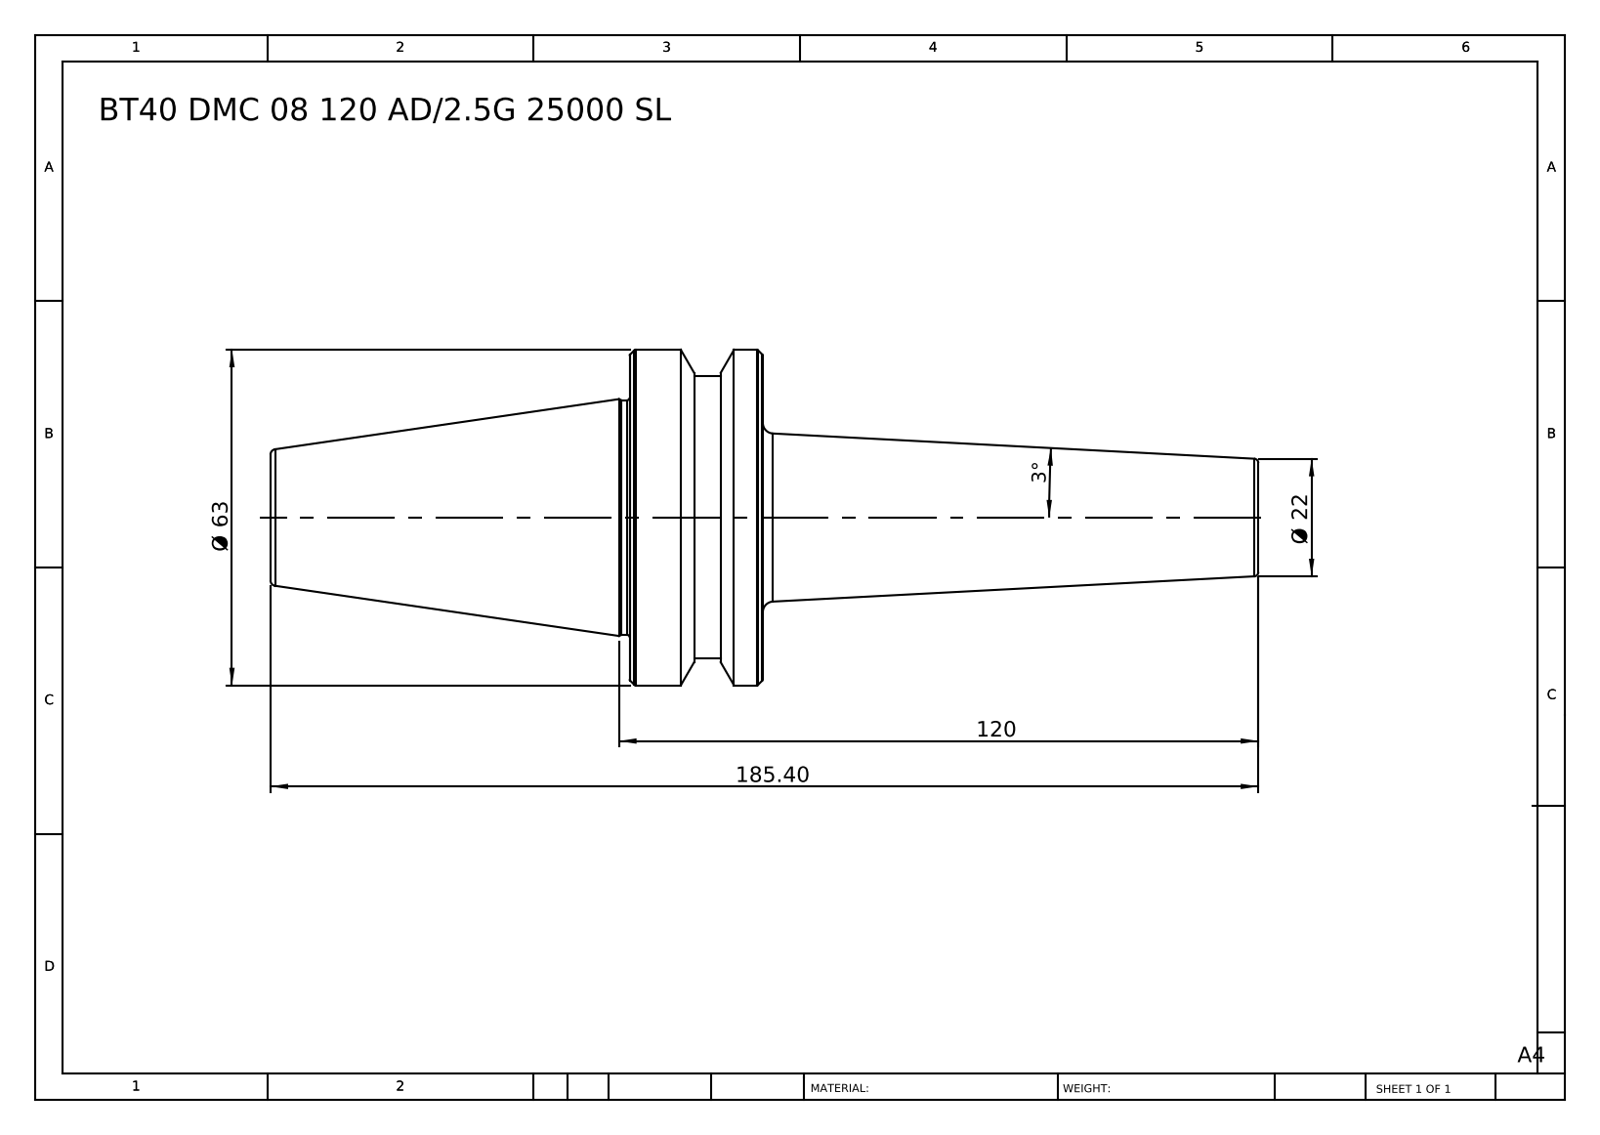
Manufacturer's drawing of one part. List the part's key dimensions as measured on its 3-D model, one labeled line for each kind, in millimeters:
Part name (STEP PRODUCT): BT40 DMC 08 120 AD-2.5G 25000 SL
STEP written by: SolidWorks 2014 (CONFIG_CONTROL_DESIGN)
Units: millimetres
Bodies: 1 solid, 44 faces (6 planar, 8 cylindrical, 30 other)
Overall size (bounding box): 185.4 × 63 × 63
Volume: 191 742 mm³ · Surface area: 25 676 mm²
Round bosses / shafts (diameter × count): ⌀63 ×1, ⌀53 ×1, ⌀44 ×1
Main face-to-face distances: 25, 92.4, 67.4, 93, 118, 185.4, 100.9, 7.9, 17.1, 84.5
